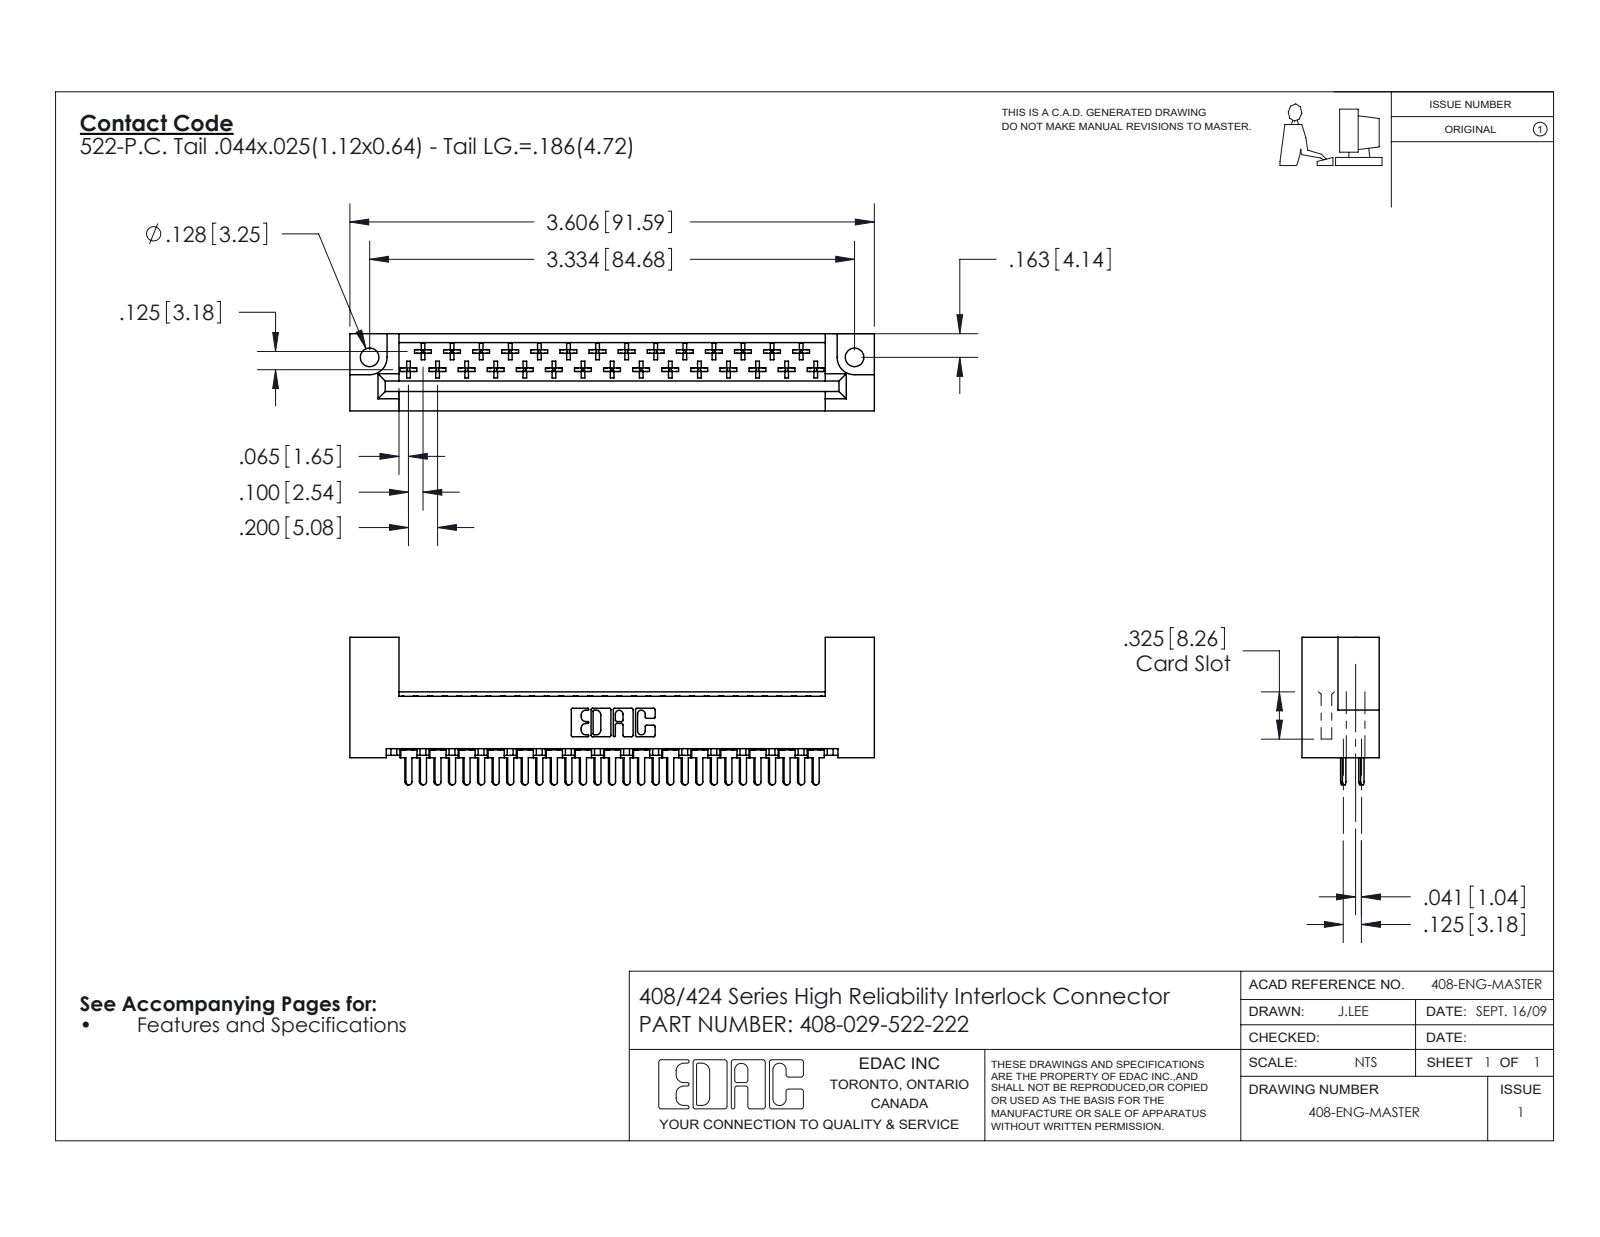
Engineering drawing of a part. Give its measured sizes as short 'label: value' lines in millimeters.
name: 408 Part_029 - 2; 408-290-001_408-290-122; 408-029-522-222
written by: SolidWorks 2016 (CONFIG_CONTROL_DESIGN)
unit: mm
bodies: 30 solids, 1737 faces (1307 planar, 314 cylindrical, 116 other)
size: 91.6 × 25.8 × 13.5
volume: 11 700 mm³; area: 13 260 mm²
holes: 2× ⌀3.3
rounds: 174× R0.3, 31× R0.5, 29× R0.6, 22× R0.3, 6× R0.2, 6× R0.8, 3× R0.7, 2× R3
face distances: 13.5, 3.2, 2.5, 0.6, 0.6, 9.2, 10.1, 6, 6.6, 5.5
hole spacings: 84.7
